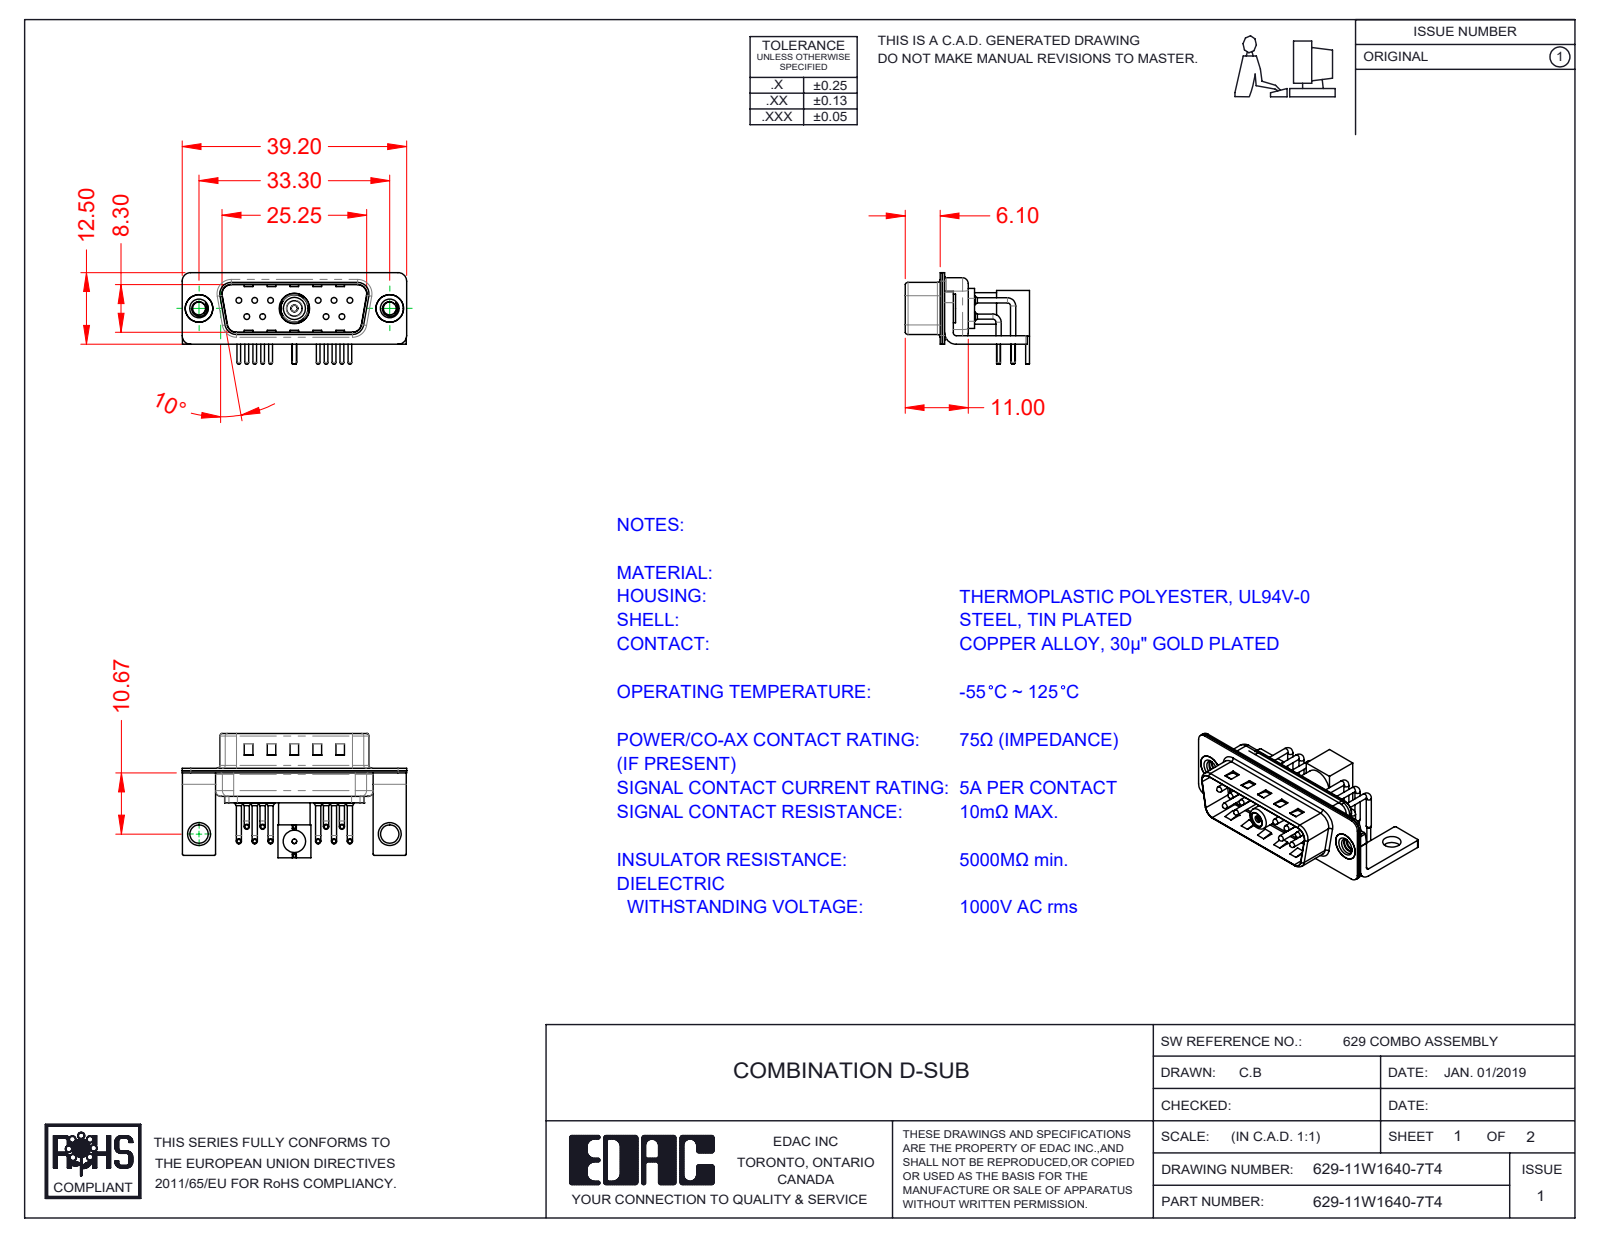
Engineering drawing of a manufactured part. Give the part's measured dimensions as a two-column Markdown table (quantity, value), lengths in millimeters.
| quantity | value |
| --- | --- |
| part name | 629-11W1640-7T4; 629Combo Contact Row 1; Insulator Socket 2; Co-Ax Jack Assy_RA (+8 more) |
| STEP written by | SolidWorks 2020 (CONFIG_CONTROL_DESIGN) |
| units | millimeters |
| bodies | 24 solids, 1645 faces (865 planar, 582 cylindrical, 198 other) |
| overall size | 39.2 × 21.71 × 16 |
| volume | 2 479 mm³ |
| surface area | 6 665 mm² |
| round holes (diameter × count) | 1.6 × 11, 0.75 × 10, 2 × 10, 2.26 × 2, 3.2 × 2, 4 × 2, 4.8 × 2, 0.8 × 1, 1.1 × 1, 1.2 × 1, 1.5 × 1, 2.5 × 1 |
| round bosses / shafts (diameter × count) | 0.9 × 20, 1.5 × 10, 1 × 10, 0.65 × 10, 5 × 2, 4.9 × 2, 0.8 × 2, 5.5 × 1 |
| partial cylindrical surfaces (radius × count) | 0.25 × 16, 1.5 × 16, 2 × 13, 1.01 × 10, 0.5 × 9, 1.6 × 8, 1 × 7, 0.6 × 4 |
| main face-to-face distances | 0.4, 0.8, 1.5, 9.5, 9.1, 9.9, 8.7, 0.6, 1.9, 0.35 |
| hole center spacings | 3.16, 2.77, 13.85, 16.7, 11.08, 16.62, 5.03, 5.04 |
